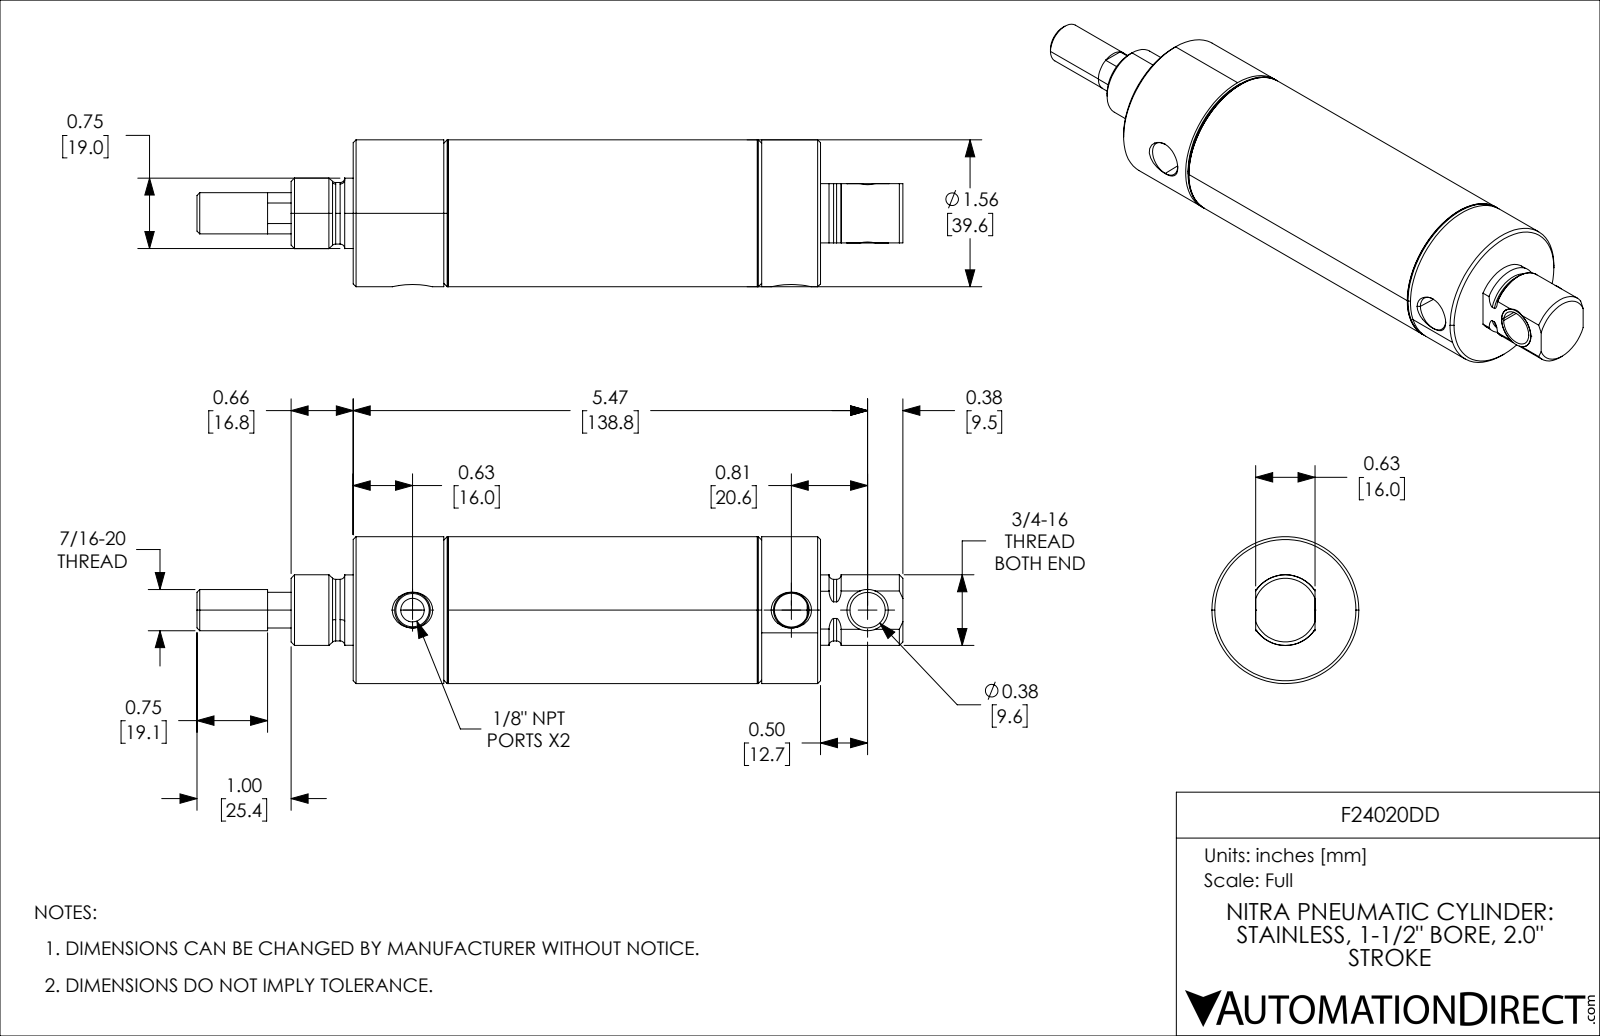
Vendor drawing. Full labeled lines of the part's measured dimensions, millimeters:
Part name (STEP PRODUCT): F24020DD_11; F24020DD_5; F24020DD_9; F24020DD_3 (+2 more)
STEP written by: SolidWorks 2021 (CONFIG_CONTROL_DESIGN)
Units: millimetres
Bodies: 5 solids, 157 faces (35 planar, 58 cylindrical, 64 other)
Overall size (bounding box): 190.5 × 39.62 × 39.62
Volume: 104 386 mm³ · Surface area: 49 838 mm²
Round holes (diameter × count): ⌀6.35 ×1, ⌀9.14 ×1, ⌀9.55 ×1, ⌀11.15 ×1, ⌀11.73 ×1, ⌀13.51 ×1, ⌀26.97 ×1, ⌀36.36 ×1
Round bosses / shafts (diameter × count): ⌀39.62 ×1, ⌀38.39 ×1, ⌀19.05 ×1, ⌀18.99 ×1, ⌀16.61 ×1, ⌀16.6 ×1, ⌀11.13 ×1, ⌀11.11 ×1
Main face-to-face distances: 22.22, 44.45, 50.8, 73.02, 95.25, 22.23, 30.86, 81.66, 103.88, 126.11
Hole centre spacings: 20.57, 102.24, 122.81
